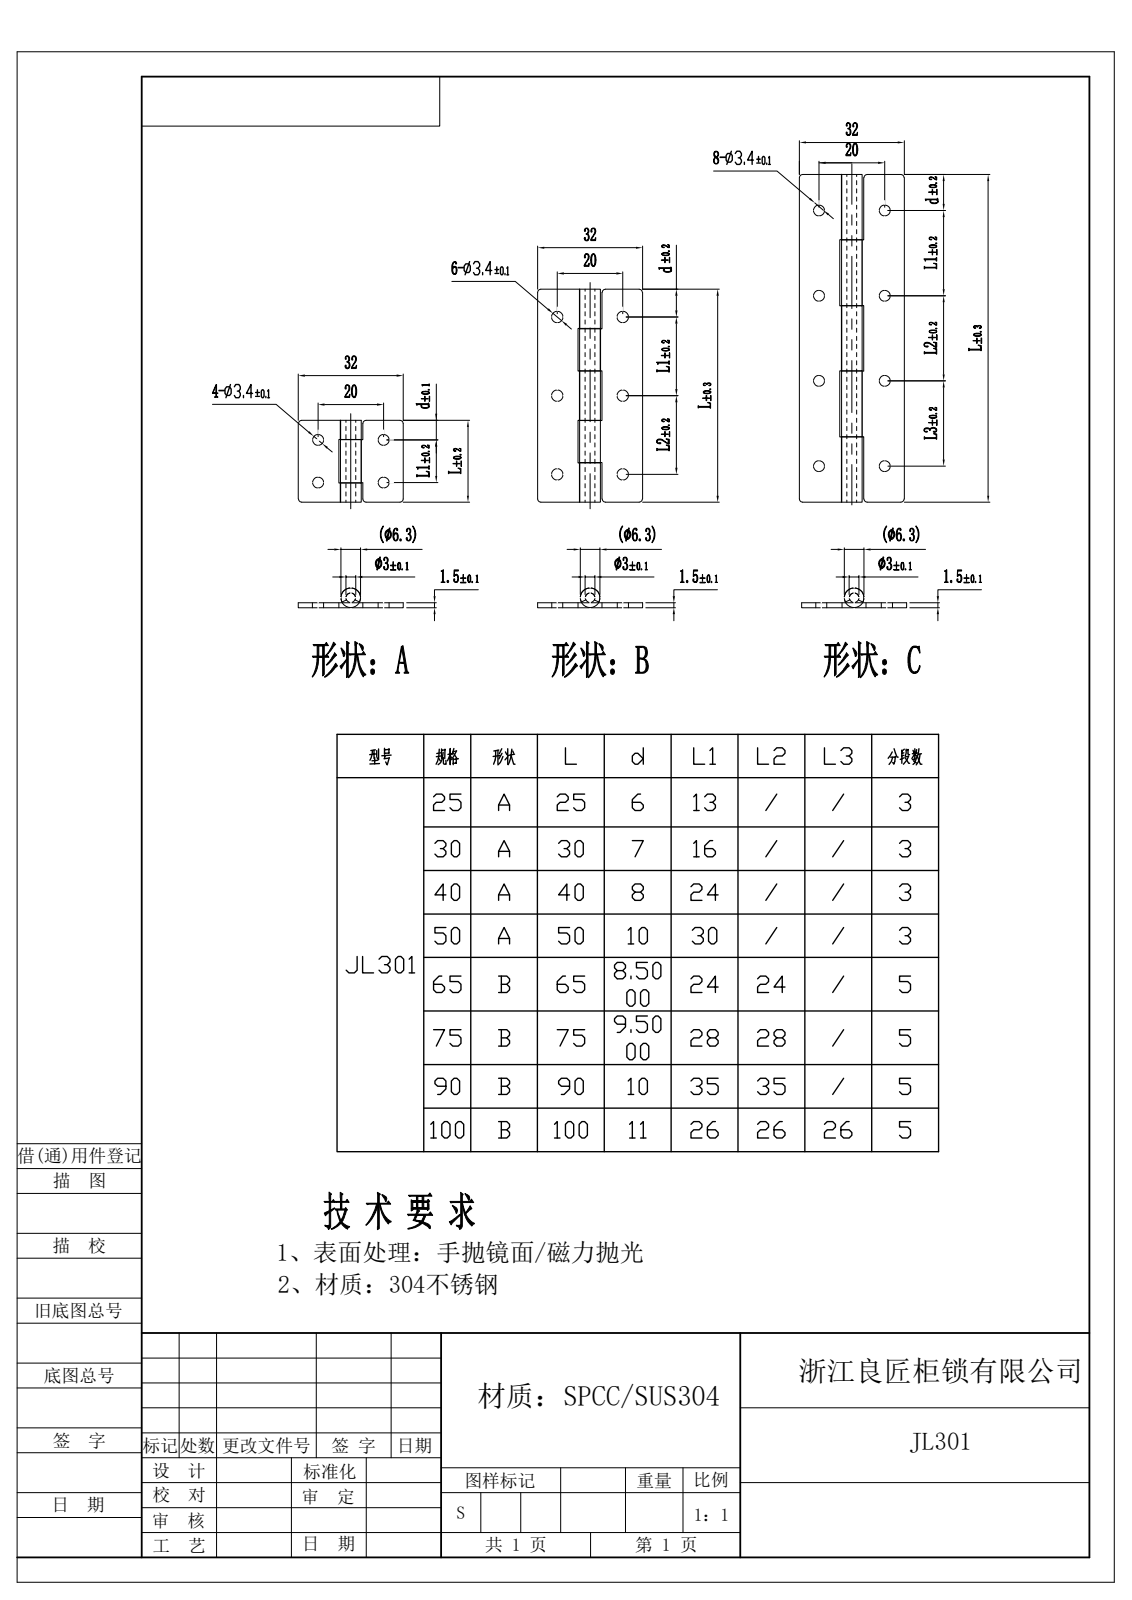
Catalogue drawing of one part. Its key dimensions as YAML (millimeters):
step_written_by: "Rhino 8.5 (CONFIG_CONTROL_DESIGN)"
units: millimeters
bodies: {solids: 61, faces: 894, planar: 552, cylindrical: 276, other: 66}
overall_size: [315.68, 108.88, 9.55]
volume: 31427
surface_area: 48668
round_holes:
  - {diameter: 3.4, count: 42}
  - {diameter: 3, count: 8}
round_bosses_or_shafts:
  - {diameter: 6, count: 8}
partial_cylinders:
  - {radius: 1, count: 48}
face_to_face_distances: [1.5, 0.92, 1.06, 1.72, 0.8, 0.66, 1.83, 2.75, 2.89, 3.55]
hole_center_spacings: [20, 24, 31.24, 28, 34.41, 80.42, 84.07, 41.14]
